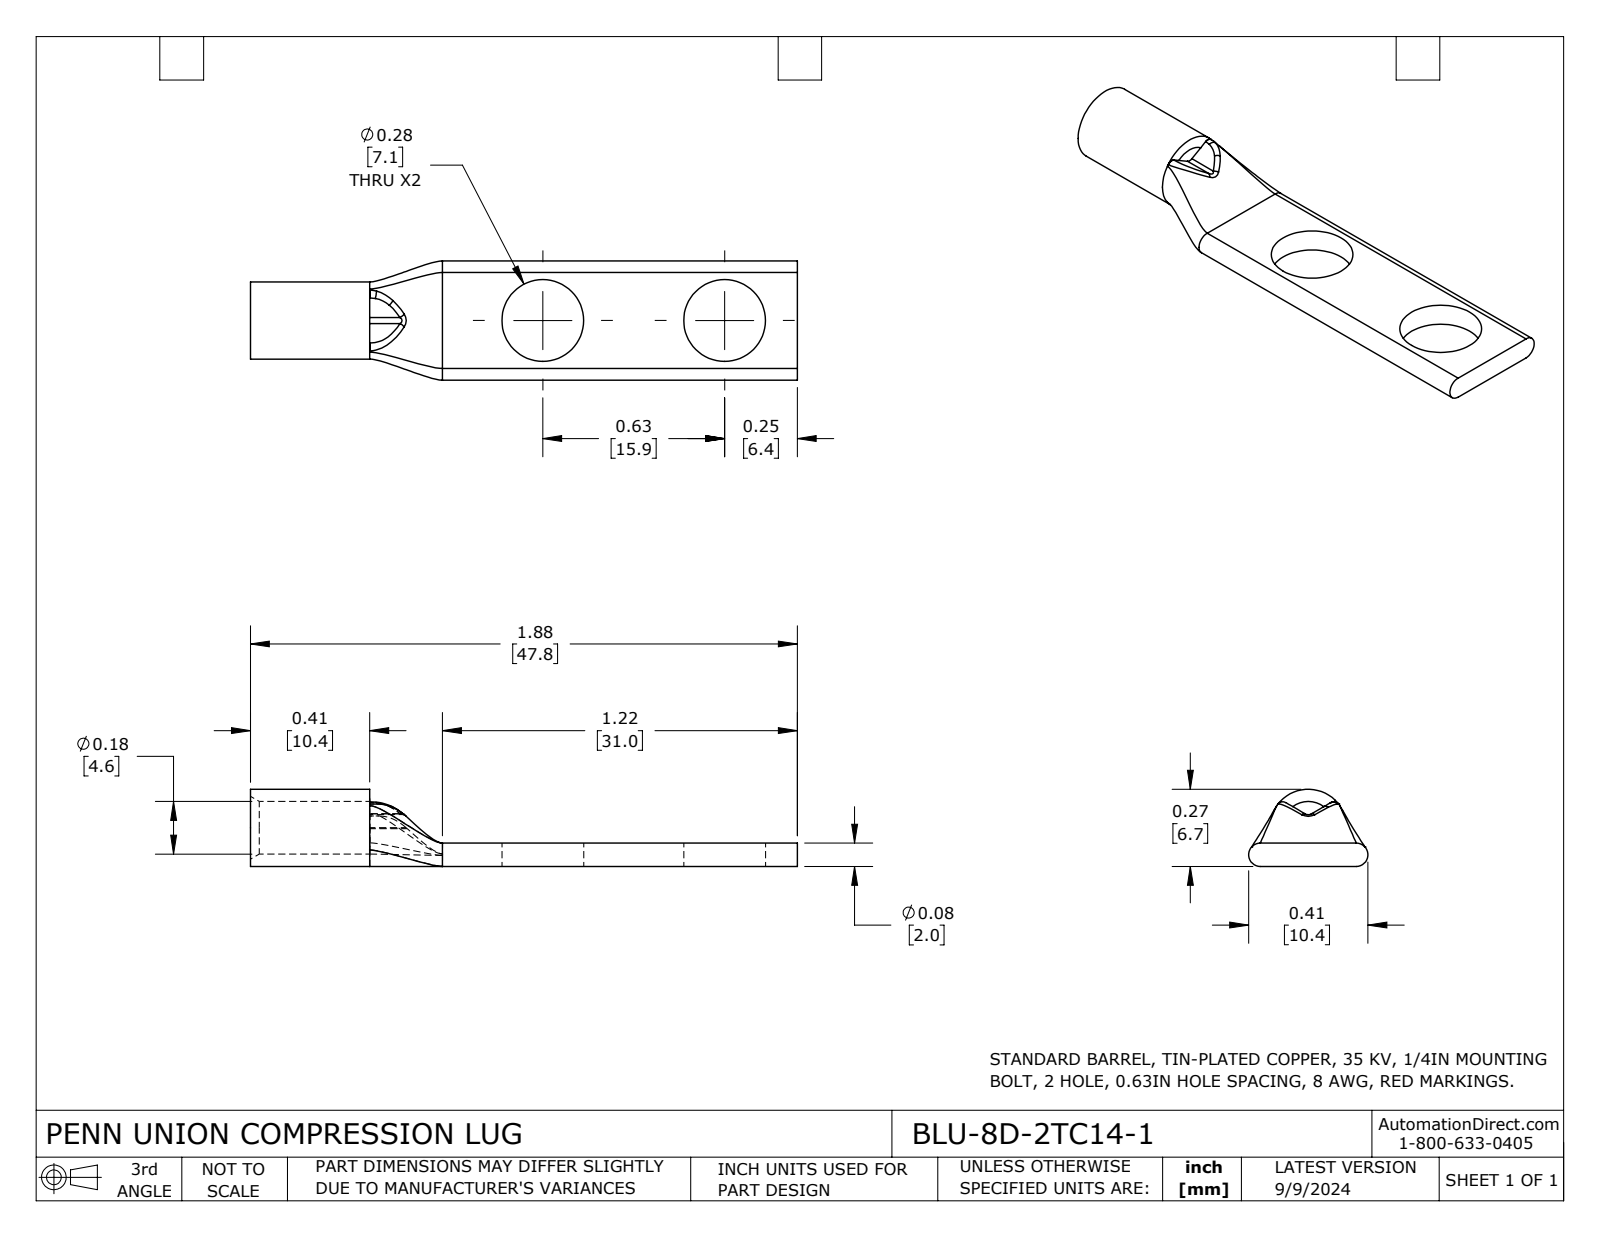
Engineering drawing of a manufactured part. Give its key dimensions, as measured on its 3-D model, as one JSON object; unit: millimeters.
{"part_name": "BLU-8D-2TC14-1", "step_written_by": "SolidWorks 2023 (CONFIG_CONTROL_DESIGN)", "units": "millimeters", "bodies": {"solids": 1, "faces": 41, "planar": 11, "cylindrical": 13, "other": 17}, "overall_size": [47.8, 10.4, 6.7], "volume_mm3": 790, "surface_area_mm2": 1317, "round_holes": [[7.1, 2], [4.6, 1]], "round_bosses_or_shafts": [[6.7, 1]], "partial_cylinders_radius": [[0.5, 2], [1, 2]], "face_to_face_distances": [2, 47.8, 10.4, 37.3, 1.1, 16.8, 6.4, 31], "hole_center_spacings": [15.9]}
